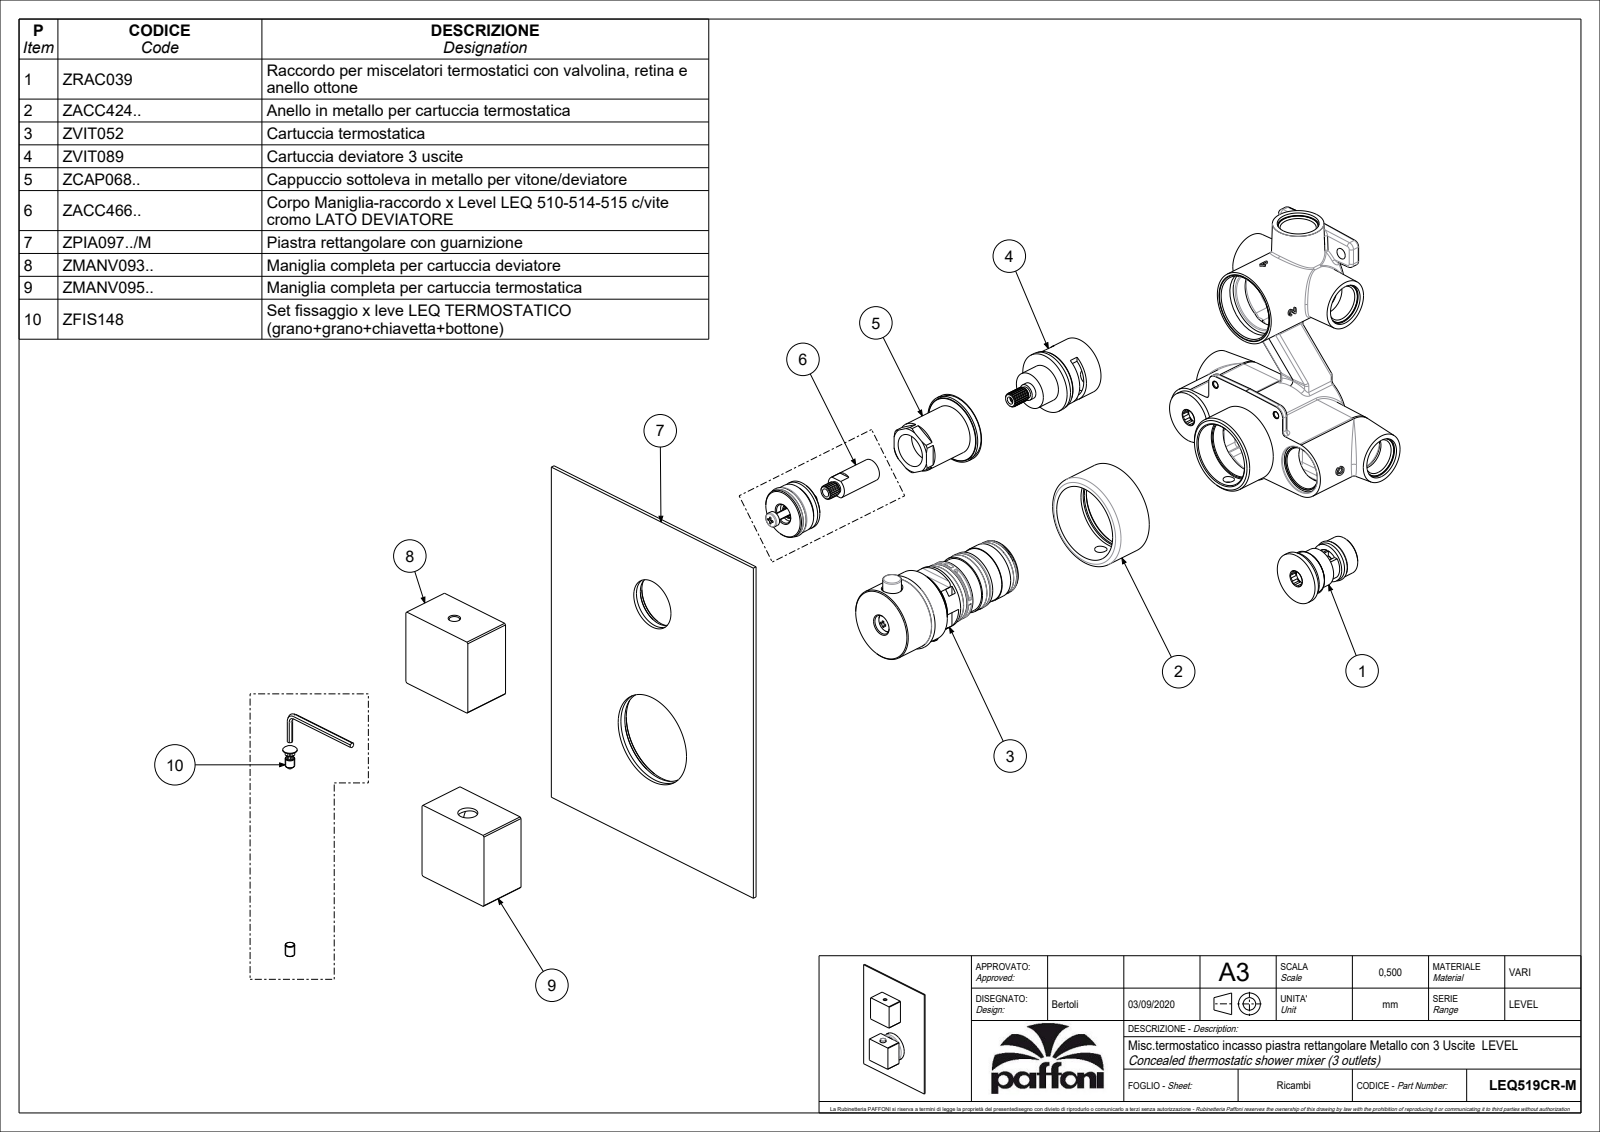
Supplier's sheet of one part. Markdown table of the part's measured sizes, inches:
| quantity | value |
| --- | --- |
| part name | LEQ518CR-M |
| STEP written by | CREO PARAMETRIC BY PTC INC, 2020044 (CONFIG_CONTROL_DESIGN) |
| units | inches |
| bodies | 1 solid, 409 faces (190 planar, 185 cylindrical, 34 other) |
| overall size | 7.874 × 5.906 × 1.575 |
| volume | 11.43 in³ |
| surface area | 129.3 in² |
| round holes (diameter × count) | 1.354 × 1, 1.409 × 1, 1.634 × 1 |
| round bosses / shafts (diameter × count) | 0.299 × 2, 1.965 × 1, 1.614 × 1, 1.535 × 1, 1.055 × 1, 0.39 × 1 |
| partial cylindrical surfaces (radius × count) | 0.006 × 60, 0.02 × 6, 0.008 × 5, 0.004 × 2, 0.031 × 2, 1.22 × 2, 0.118 × 1, 0.128 × 1 |
| main face-to-face distances | 0.079, 1.693, 3.228, 1.811, 1.457, 1.378, 1.575, 1.496, 0.118, 0.355 |
